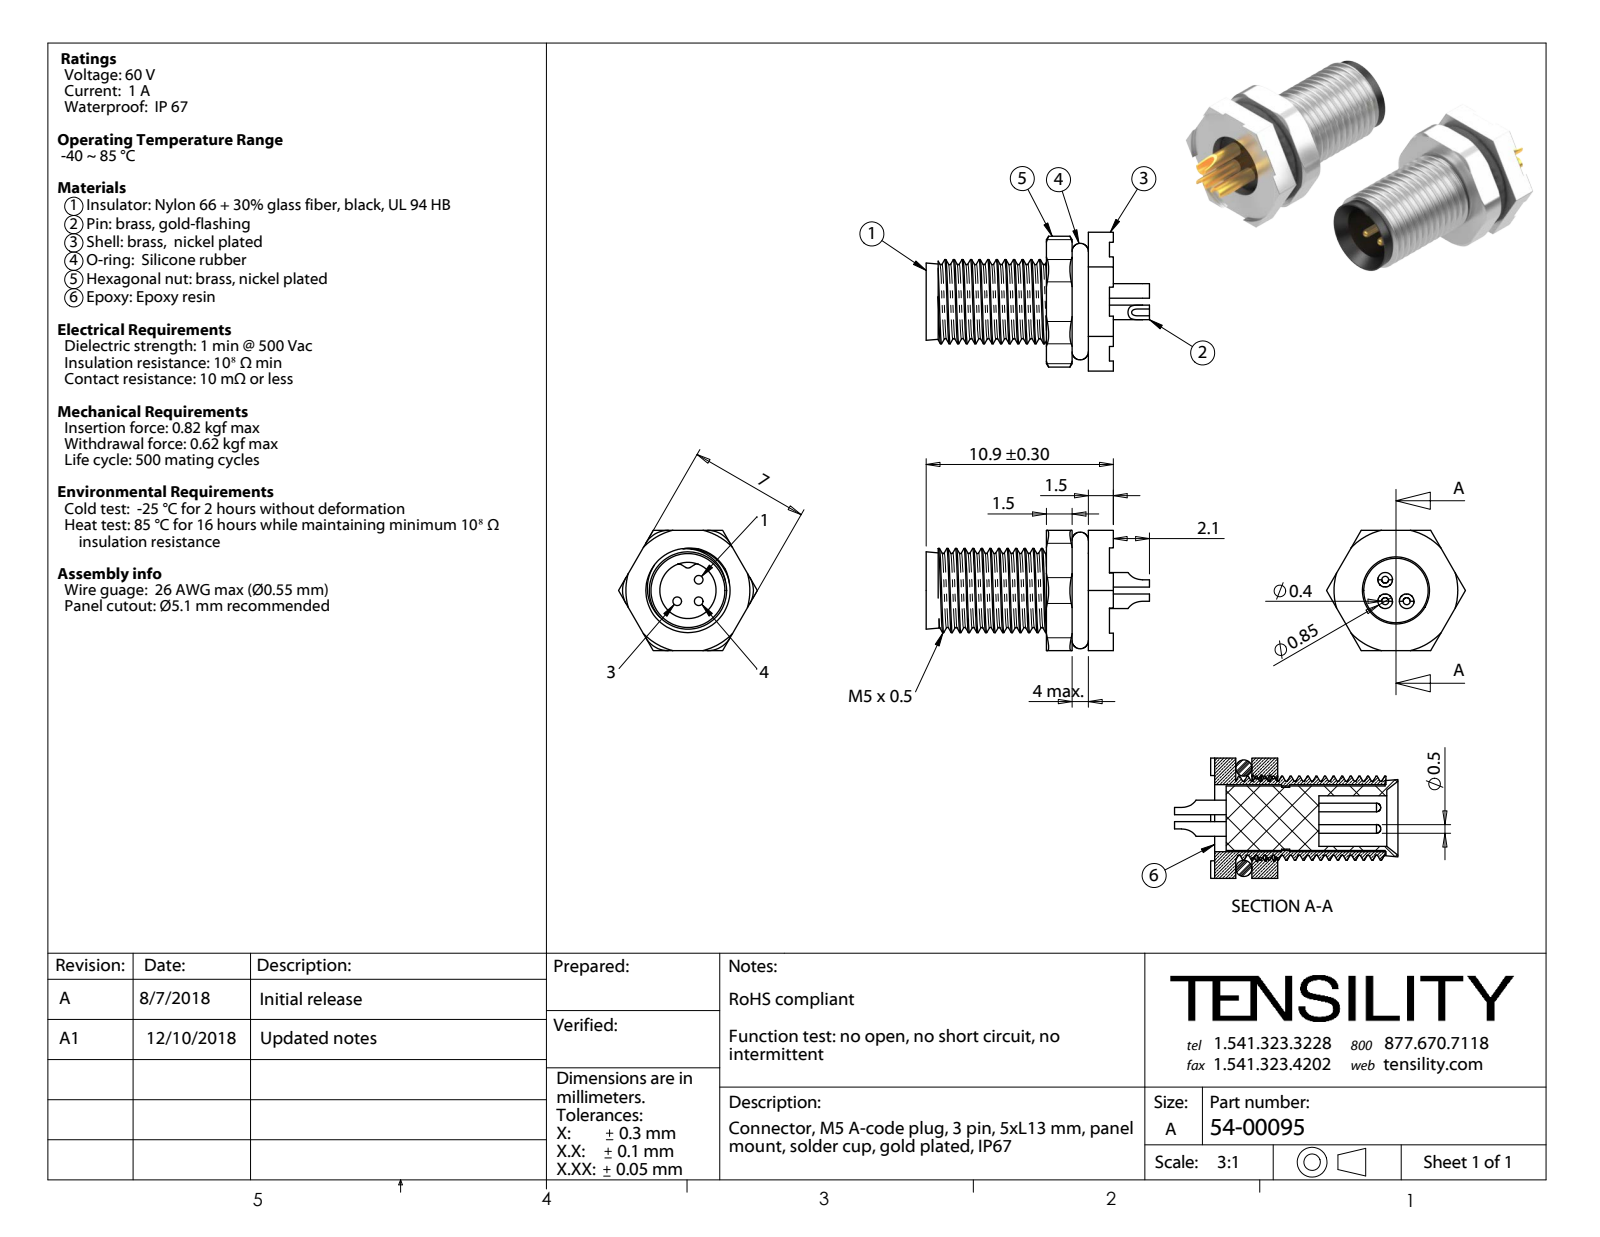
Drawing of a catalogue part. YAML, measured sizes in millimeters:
part_name: "M5_oring_large; M5M3P_short; M5Male_pin_M5Male_pin; M5nut (+2 more)"
step_written_by: "SolidWorks 2021 (CONFIG_CONTROL_DESIGN)"
units: millimeters
bodies: {solids: 7, faces: 182, planar: 44, cylindrical: 101, other: 37}
overall_size: [13.3, 8.08, 7]
volume: 208
surface_area: 927
round_holes:
  - {diameter: 0.4, count: 3}
  - {diameter: 0.5, count: 3}
  - {diameter: 0.85, count: 3}
  - {diameter: 3.28, count: 1}
  - {diameter: 3.6, count: 1}
  - {diameter: 3.9, count: 1}
  - {diameter: 4.6, count: 1}
round_bosses_or_shafts:
  - {diameter: 4.9, count: 1}
  - {diameter: 3.75, count: 1}
partial_cylinders:
  - {radius: 1.5, count: 6}
  - {radius: 0.25, count: 3}
  - {radius: 3.6, count: 1}
face_to_face_distances: [1.5, 7, 1.23, 2.17, 0.94, 3.67, 2.44, 3.9, 2.4, 3]
hole_center_spacings: [0.89, 1.26, 1.78]
